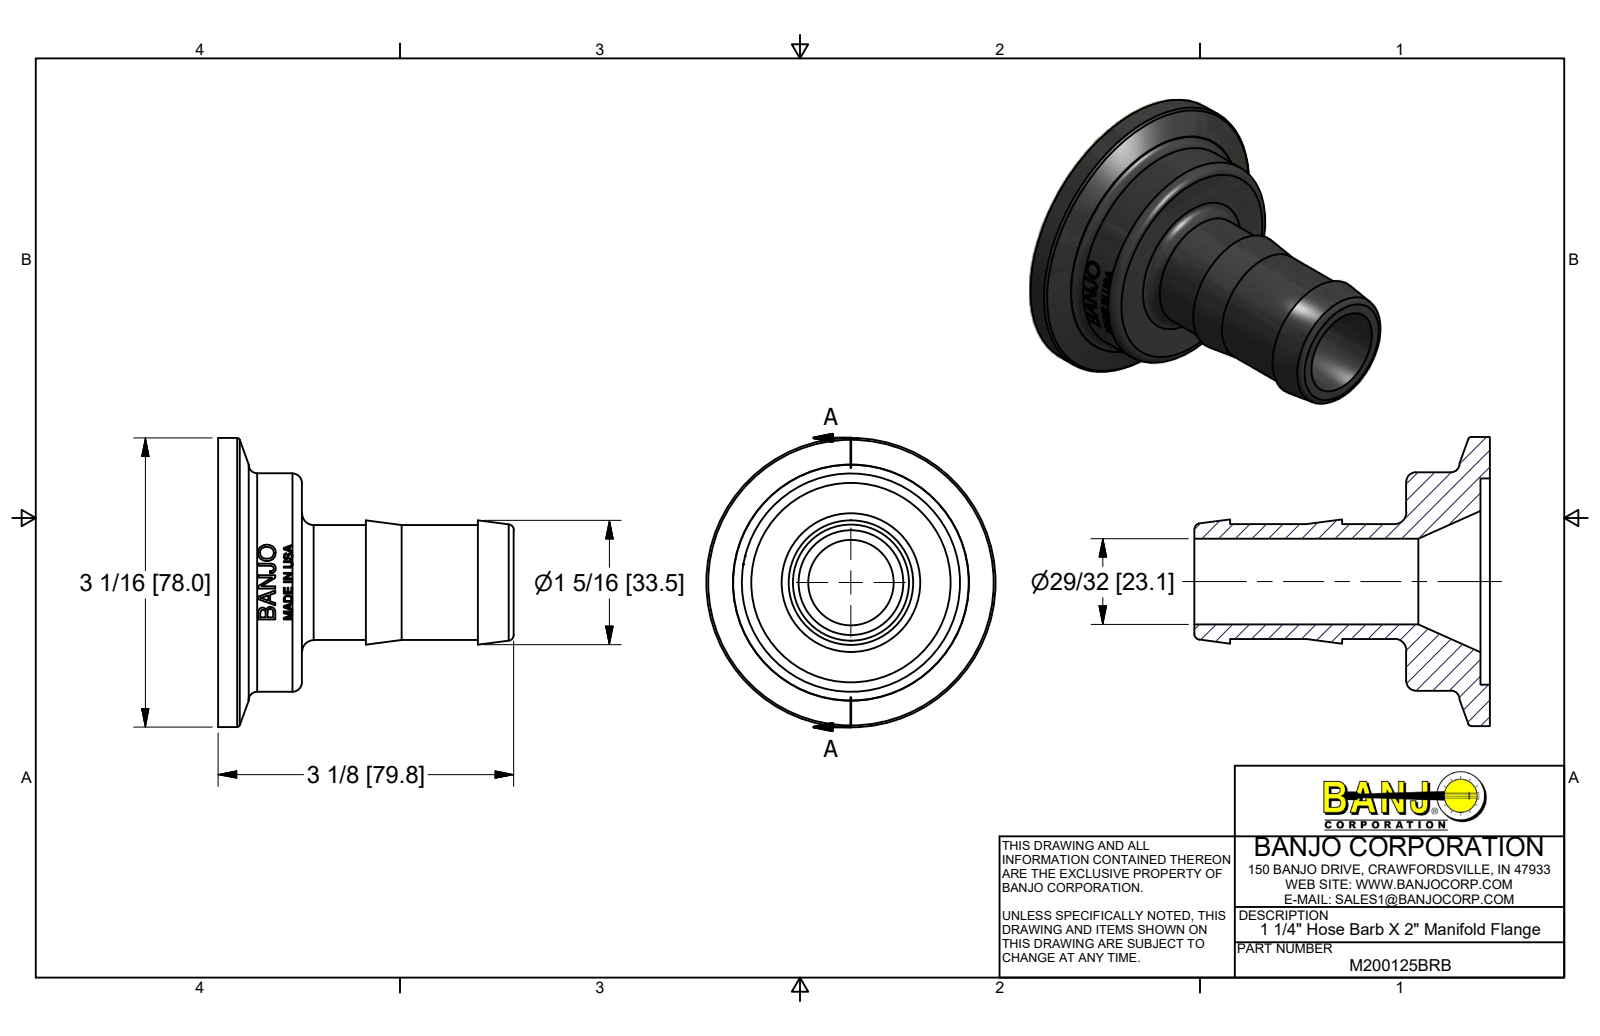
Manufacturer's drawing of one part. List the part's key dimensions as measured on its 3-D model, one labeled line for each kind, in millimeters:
Part name (STEP PRODUCT): M200125BRB
STEP written by: Autodesk Inventor 2014 (AUTOMOTIVE_DESIGN)
Units: millimetres
Bodies: 1 solid, 399 faces (193 planar, 44 cylindrical, 162 other)
Overall size (bounding box): 79.76 × 77.98 × 77.98
Volume: 76 643 mm³ · Surface area: 24 424 mm²
Round holes (diameter × count): ⌀23.11 ×1, ⌀55.63 ×1
Round bosses / shafts (diameter × count): ⌀77.98 ×1, ⌀58.93 ×1, ⌀30.99 ×1
Partial cylindrical surfaces — rounded edges, fillets, slot ends (radius × count): R28.7 ×1
Main face-to-face distances: 2.54, 20.07, 22.61, 39.88, 57.15, 77.22, 79.76, 9.65, 47.5, 67.57
